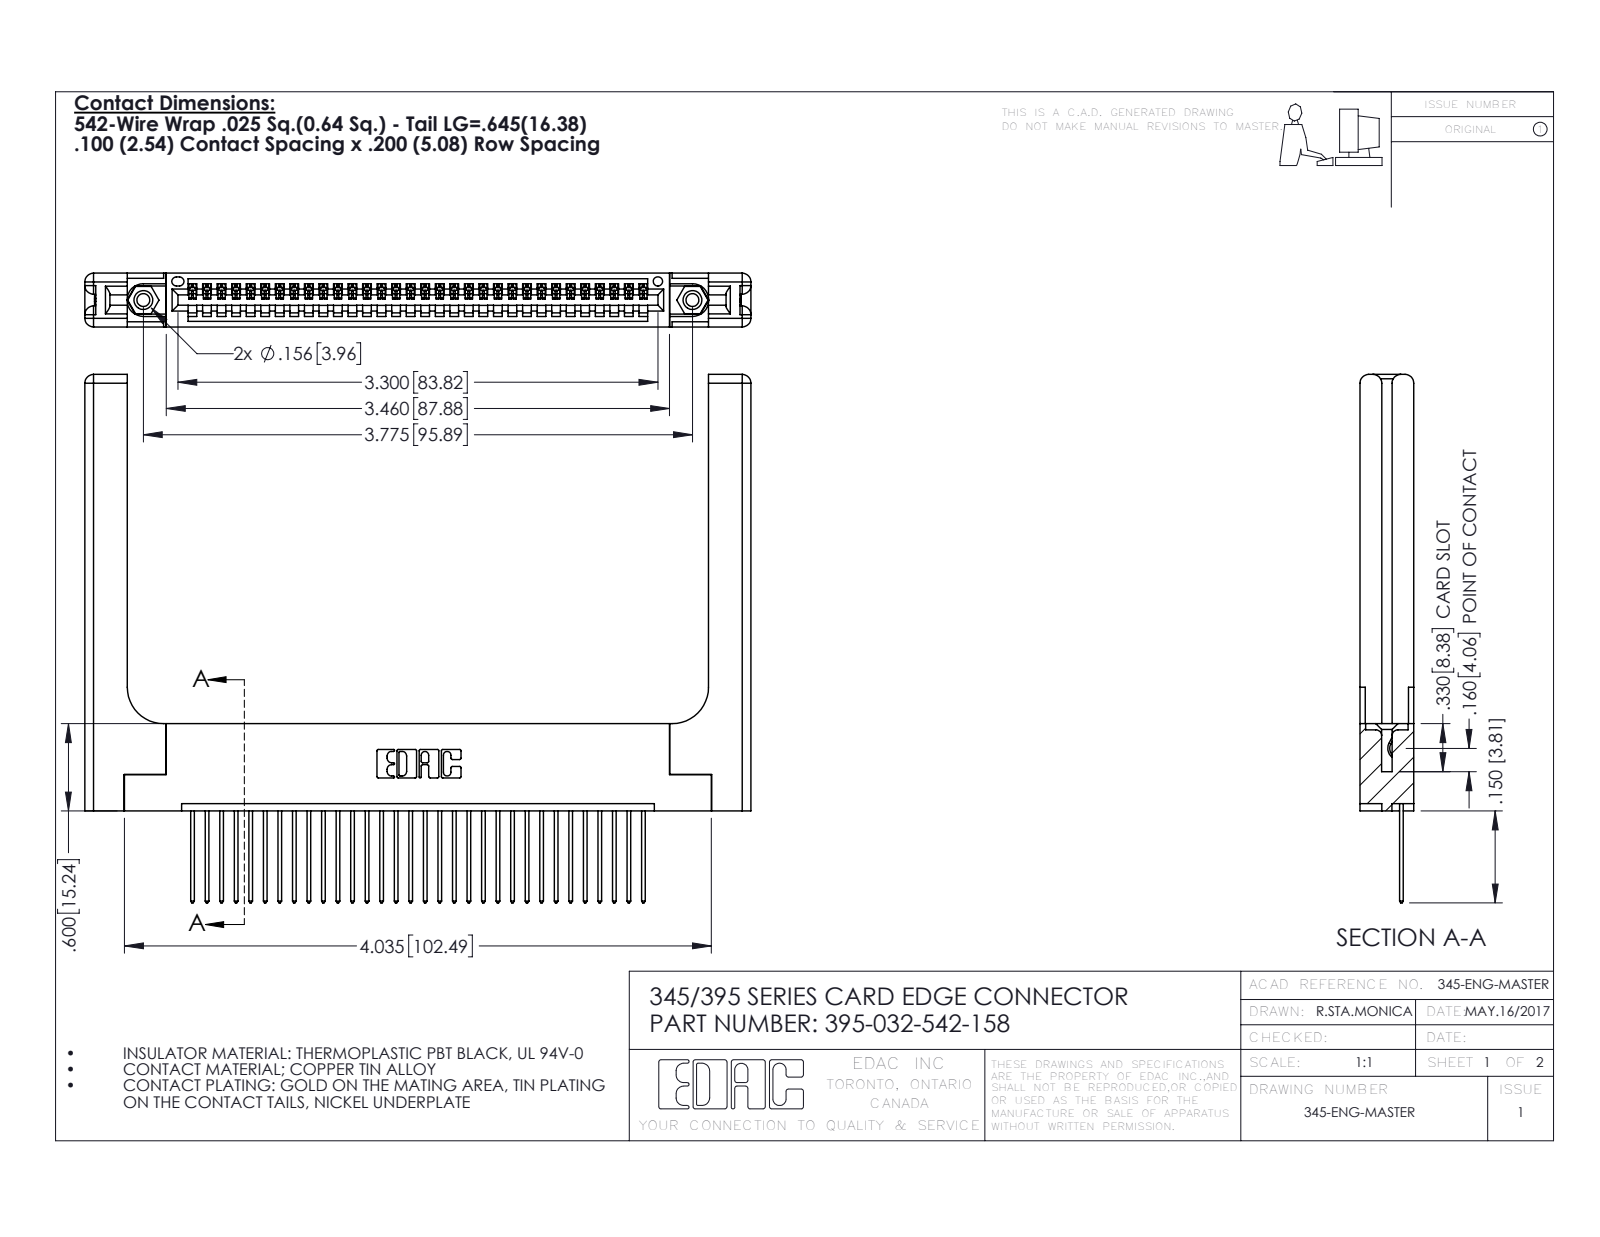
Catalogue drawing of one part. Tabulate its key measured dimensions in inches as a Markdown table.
| quantity | value |
| --- | --- |
| part name | 345 Part_Flush Mounting Lugs - 0.156 Dia-TH; 345-220-058_345-220-058; 345-250-001_345-250-001-102; 395-032-542-158 (+1 more) |
| STEP written by | SolidWorks 2016 (CONFIG_CONTROL_DESIGN) |
| units | inches |
| bodies | 37 solids, 2238 faces (1508 planar, 670 cylindrical, 60 other) |
| overall size | 4.579 × 3.632 × 0.37 |
| volume | 1.192 in³ |
| surface area | 31.44 in² |
| round holes (diameter × count) | 0.089 × 2, 0.125 × 2, 0.156 × 2, 0.064 × 1 |
| round bosses / shafts (diameter × count) | 0.155 × 2 |
| partial cylindrical surfaces (radius × count) | 0.006 × 64, 0.01 × 64, 0.01 × 22, 0.06 × 16, 0.007 × 6, 0.031 × 6, 0.026 × 3, 0.03 × 2 |
| main face-to-face distances | 0.37, 0.072, 0.298, 0.2, 0.098, 0.272, 0.025, 0.148, 0.15, 0.077 |
| hole center spacings | 0.27, 3.54, 3.775 |
